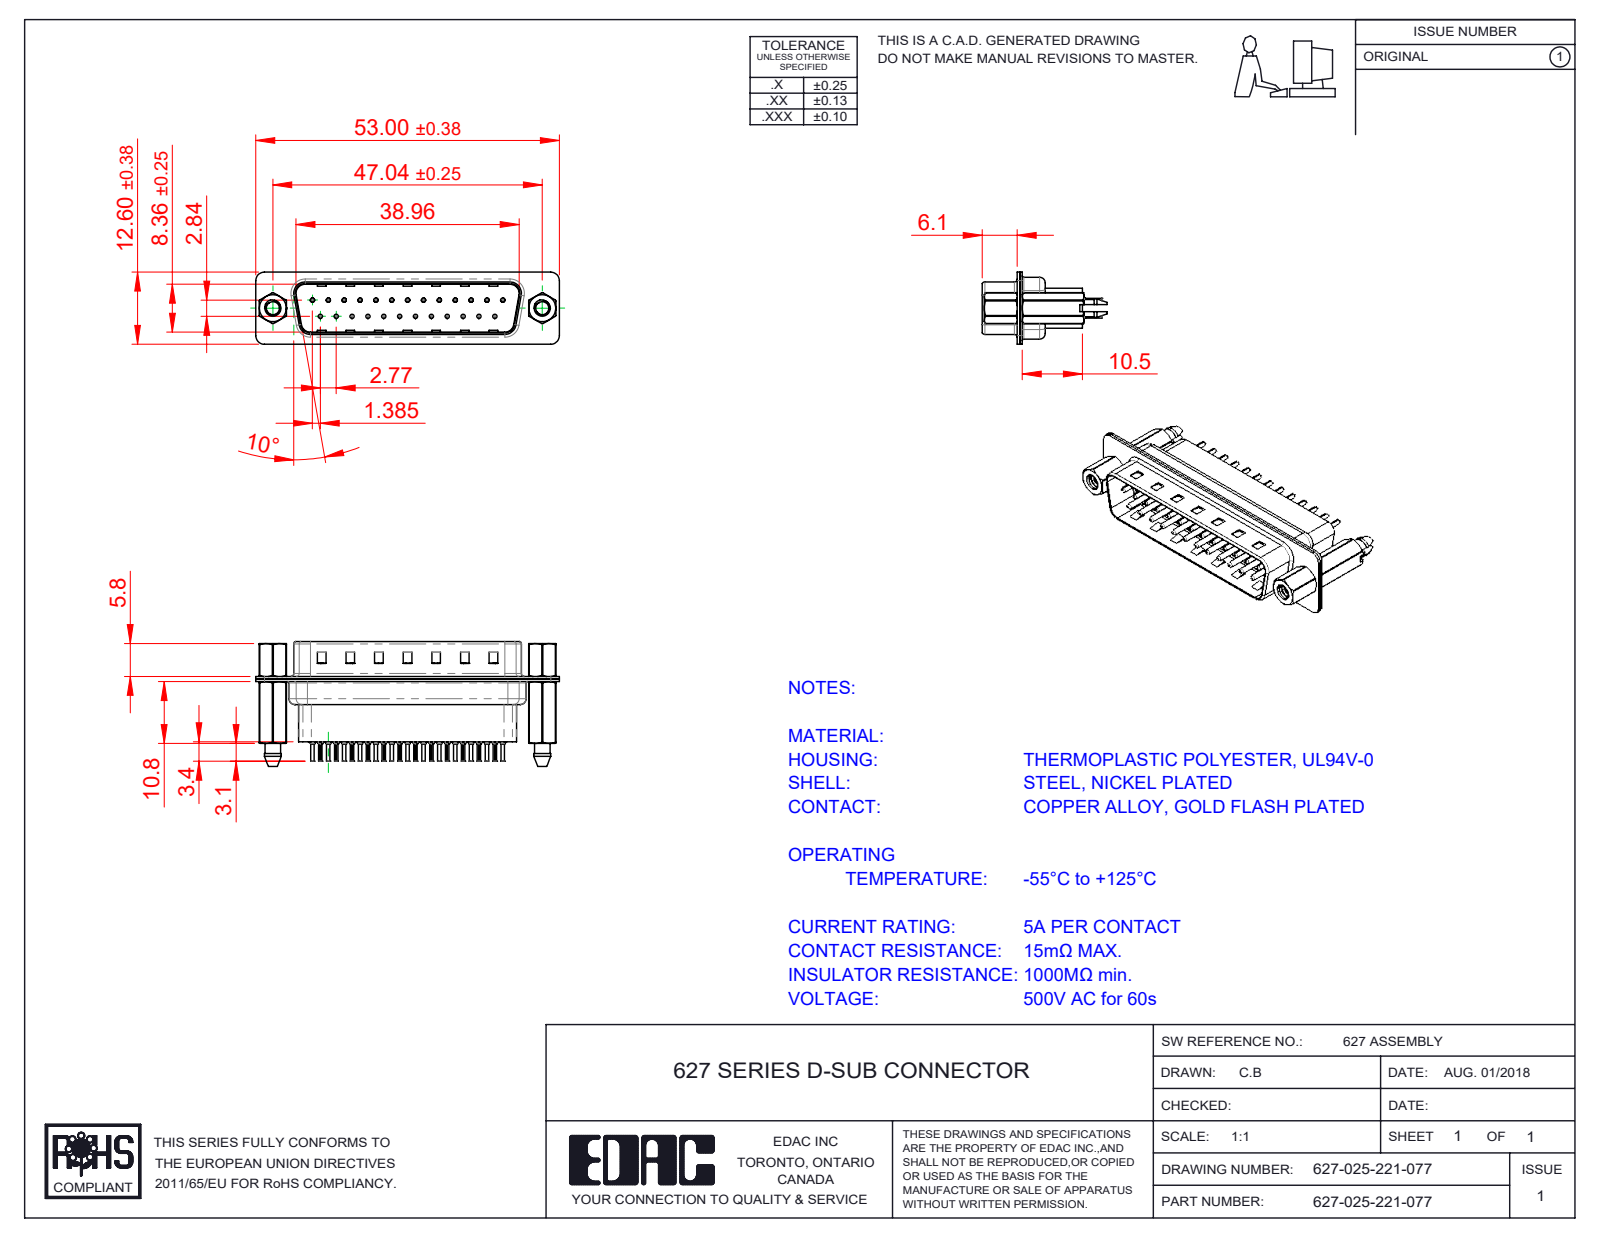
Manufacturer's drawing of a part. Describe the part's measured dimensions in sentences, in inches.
The part is named "627 4-40 Threaded Boardlock_HP; 627-025-221-077; 627 4-40 Hex Standoff; 627 Housing_25 HP (+4 more)". Its 3-D file was written by "SolidWorks 2020 (CONFIG_CONTROL_DESIGN)". It is 32 solids with 3066 faces: 825 planar, 1202 cylindrical and 1039 other. Overall it measures 2.087 by 0.854 by 0.496 inches. Its volume is 0.26 cubic inches and its surface area 16.81 square inches. Round holes: 25 of diameter 0.008, 25 of diameter 0.014, 25 of diameter 0.043, 25 of diameter 0.063, 2 of diameter 0.089, 2 of diameter 0.09, 2 of diameter 0.157, 2 of diameter 0.189. Round bosses or shafts: 25 of diameter 0.079, 25 of diameter 0.059, 25 of diameter 0.03, 25 of diameter 0.024, 2 of diameter 0.193, 2 of diameter 0.11. Partial cylindrical surfaces (rounded edges, fillets, slot ends): 50 of radius 0.004, 18 of radius 0.059, 12 of radius 0.079, 10 of radius 0.063, 8 of radius 0.02, 4 of radius 0.01, 4 of radius 0.024, 4 of radius 0.026. The main face-to-face distances are 0.016, 0.018, 0.032, 0.377, 0.027, 0.302, 0.059, 0.035, 0.043, 0.318. The hole center spacings are 0.124, 0.327, 0.109, 0.218, 0.436, 0.654, 0.198, 0.198.
